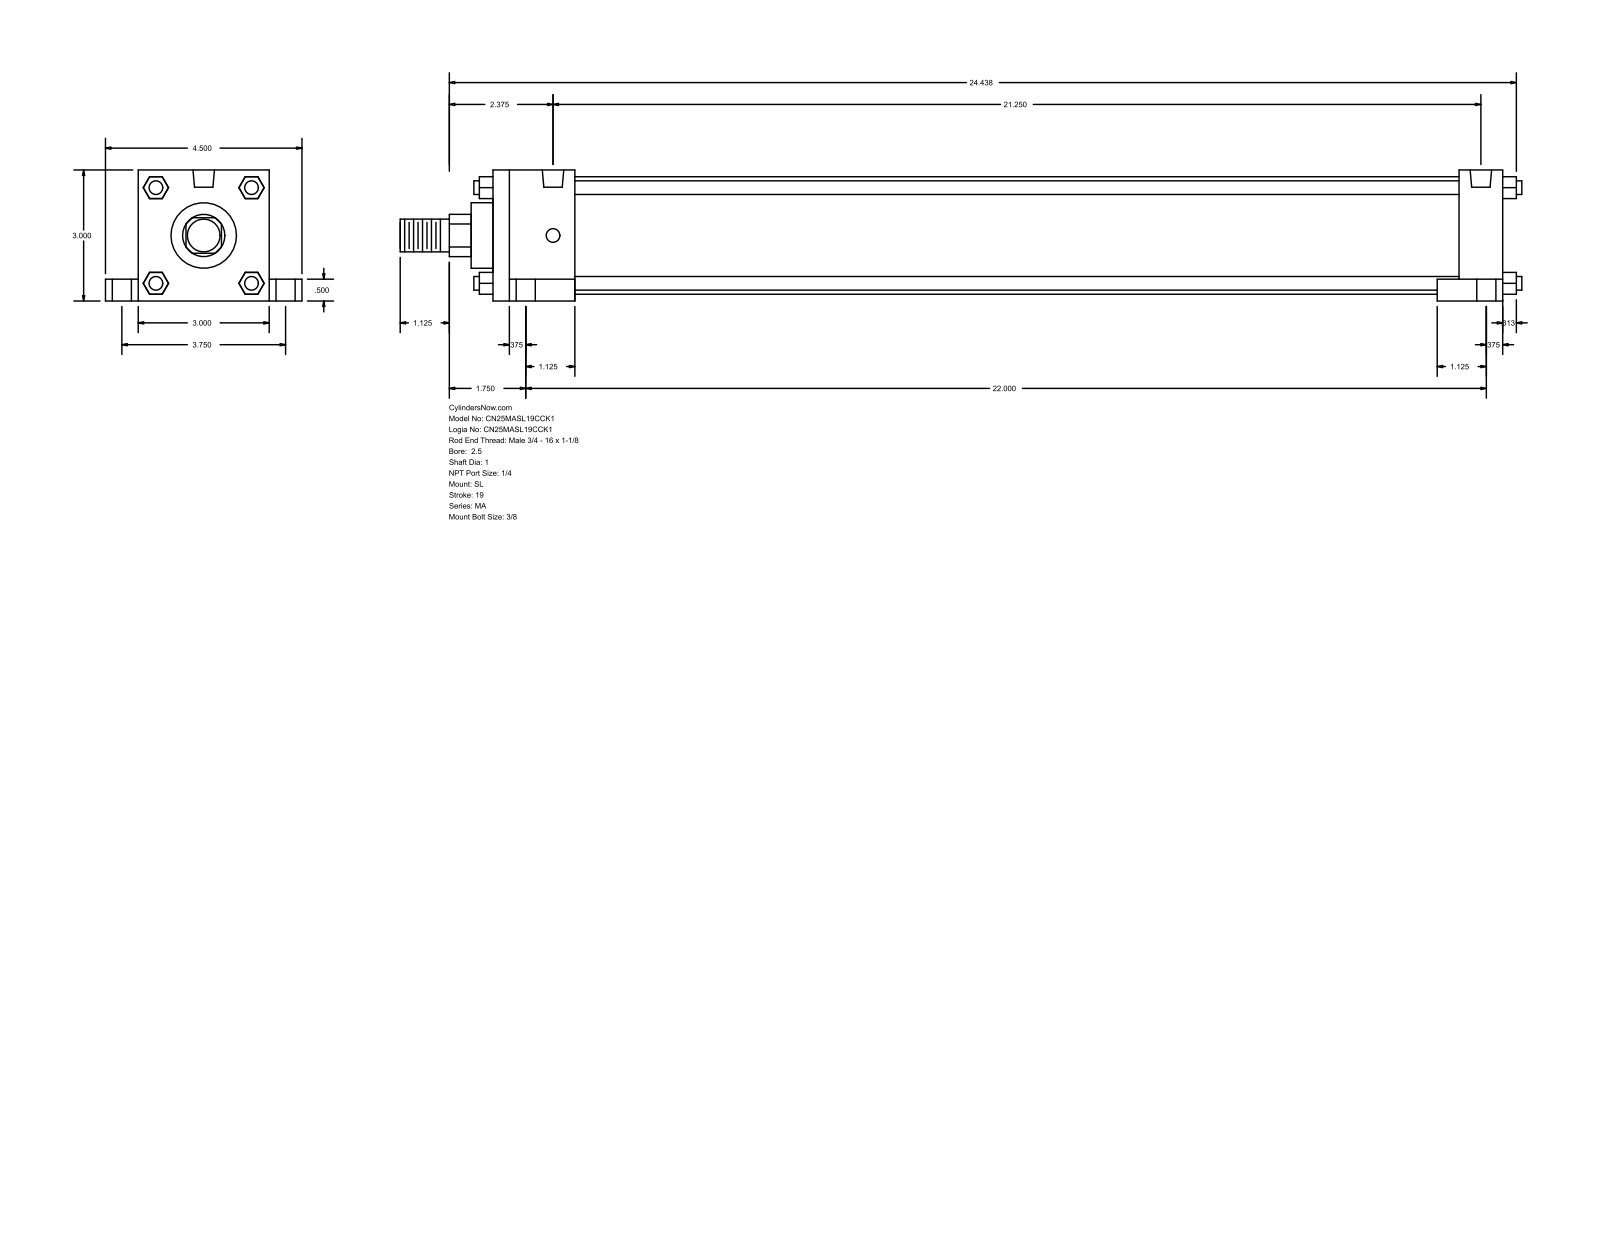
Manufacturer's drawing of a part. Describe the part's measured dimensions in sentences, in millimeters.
The part is named "MA_SL__0250_1". Its 3-D file was written by "GSSL Pune (CONFIG_CONTROL_DESIGN)". It is 0 solids with 148 faces: 112 planar, 36 cylindrical and 0 other. Overall it measures 652.46 by 114.3 by 76.2 millimeters. Round holes: 4 of diameter 7.94, 4 of diameter 11.11, 4 of diameter 17.46, 2 of diameter 12.49. Round bosses or shafts: 4 of diameter 7.94, 1 of diameter 68.33, 1 of diameter 38.1, 1 of diameter 25.4, 1 of diameter 19.05. Partial cylindrical surfaces (rounded edges, fillets, slot ends): 1 of radius 12.29. The main face-to-face distances are 76.2, 587.37, 12.7, 514.35, 25.39, 47.63, 539.74, 561.98, 19.05, 95.25. The hole center spacings are 47.73, 50.2, 95.24, 539.75, 545, 557.67, 558.8, 566.86.
